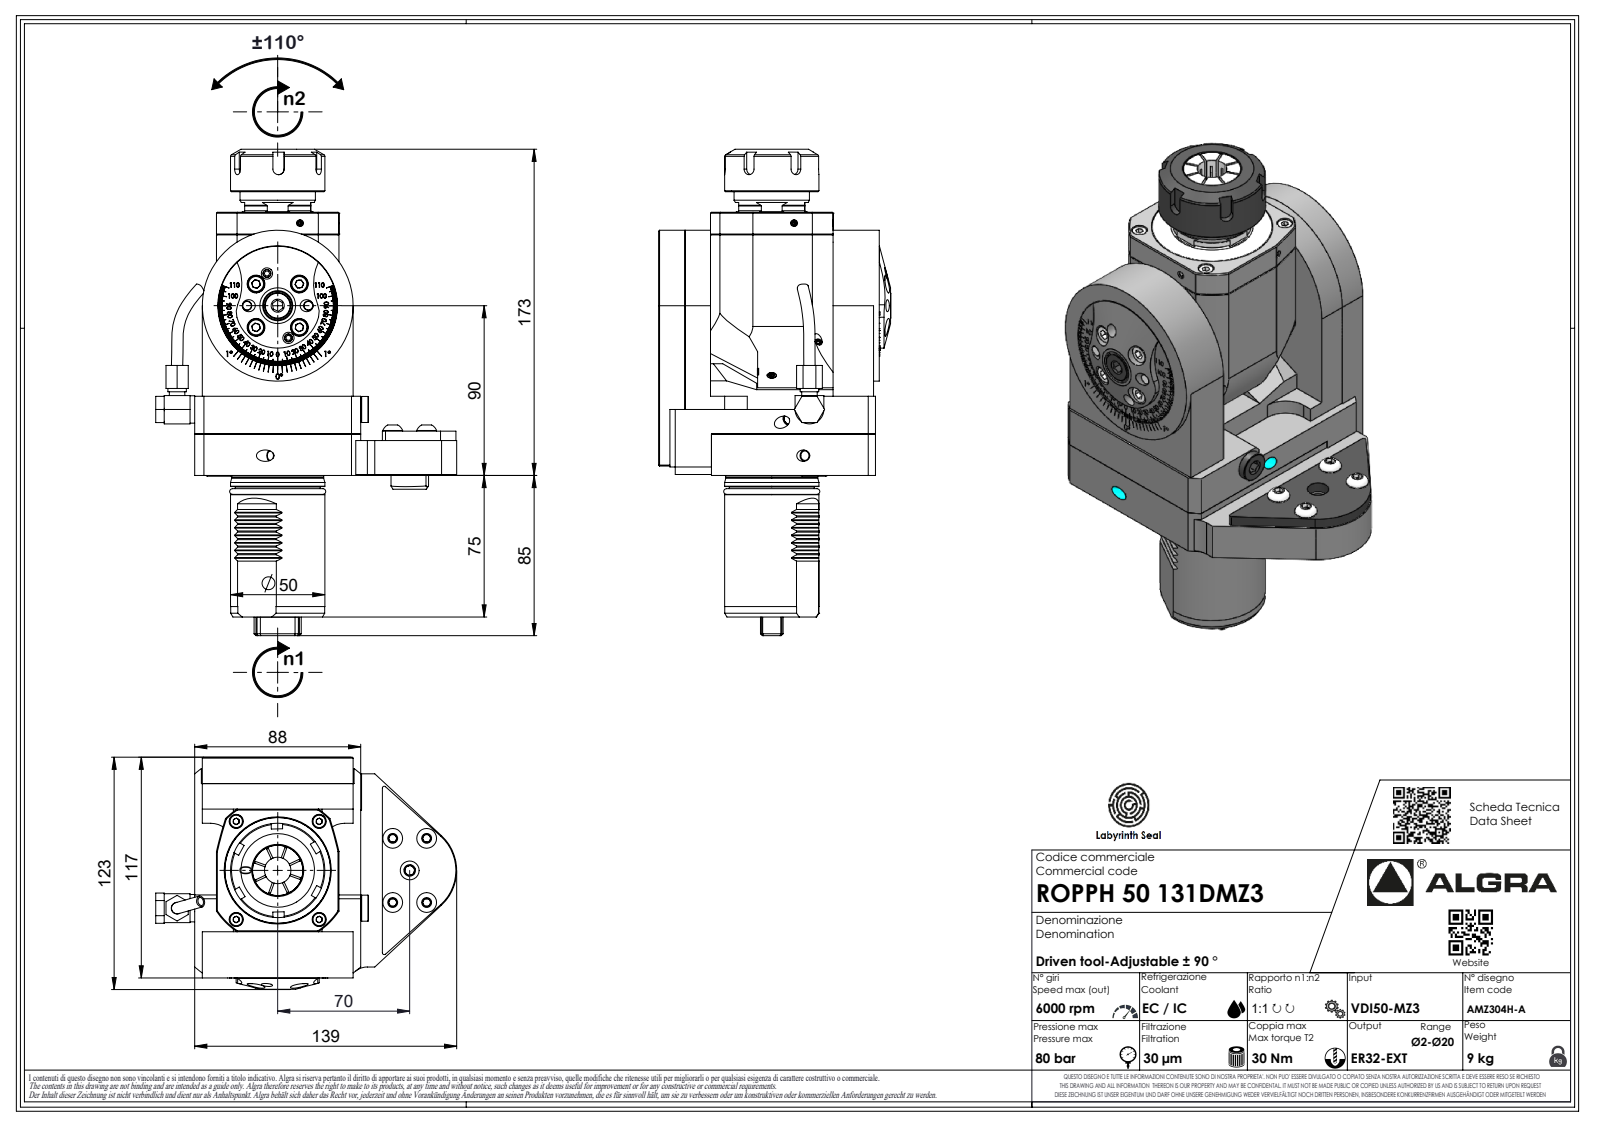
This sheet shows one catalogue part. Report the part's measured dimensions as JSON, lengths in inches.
{"part_name": "ROPPH50131DMZ3", "step_written_by": "SolidWorks 2023 (AUTOMOTIVE_DESIGN)", "units": "inches", "bodies": {"solids": 2, "faces": 640, "planar": 402, "cylindrical": 104, "other": 134}, "overall_size": [10.15, 6.285, 4.843], "volume_in3": 82.99, "surface_area_in2": 184.3, "round_holes": [[0.083, 1]], "round_bosses_or_shafts": [[0.413, 4], [3.15, 1], [1.969, 1], [1.963, 1], [1.917, 1], [1.772, 1], [1.575, 1], [0.787, 1]], "partial_cylinders_radius": [[0.012, 7], [0.013, 7], [0.02, 7], [0.146, 7], [0.079, 6], [0.118, 5], [0.394, 3], [0.039, 2]], "face_to_face_distances": [0.157, 0.453, 0.02, 2.559, 3.307, 4.606, 3.15, 0.886, 0.295, 3.012]}
